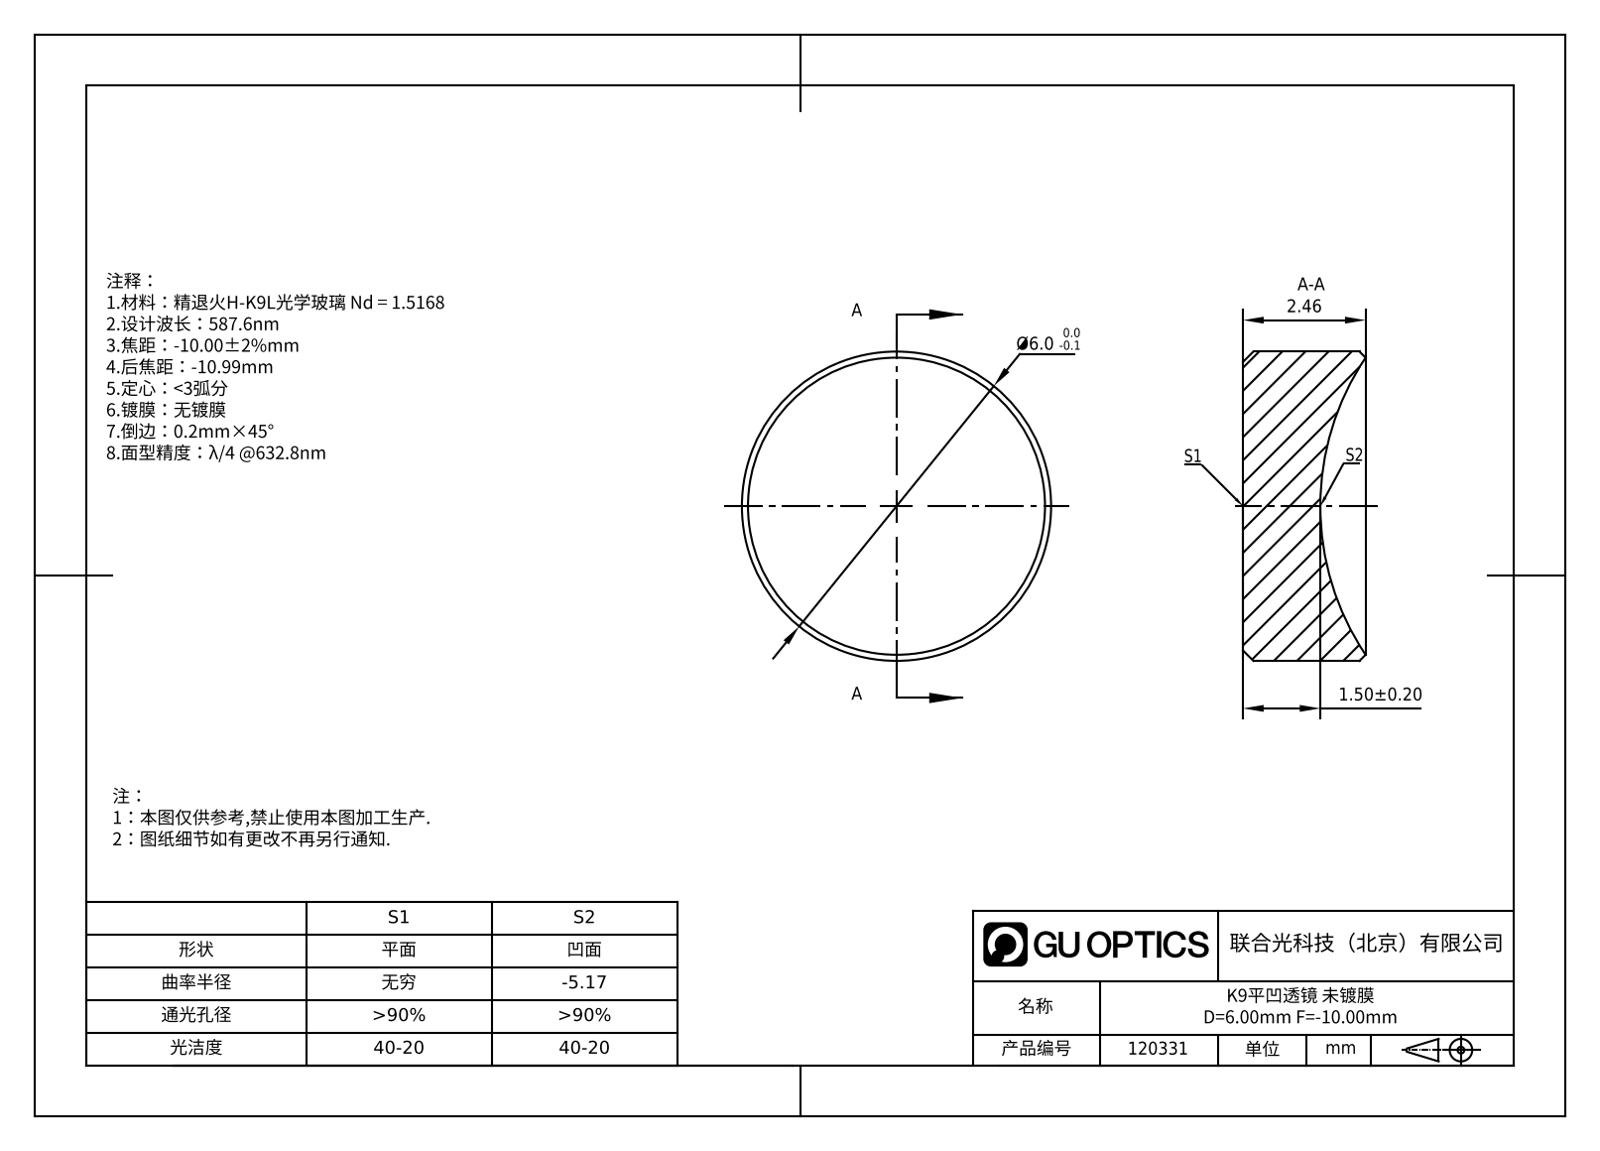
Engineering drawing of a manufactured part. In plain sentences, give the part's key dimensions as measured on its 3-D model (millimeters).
The part is named "GL13-006A-010". Its 3-D file was written by "SolidWorks 2022 (AUTOMOTIVE_DESIGN)". It is 1 solid with 9 faces: 1 planar, 2 cylindrical and 6 other. Overall it measures 6 by 6 by 2.38 millimeters. Its volume is 55 cubic millimeters and its surface area 100 square millimeters. Round bosses or shafts: 1 of diameter 6.
